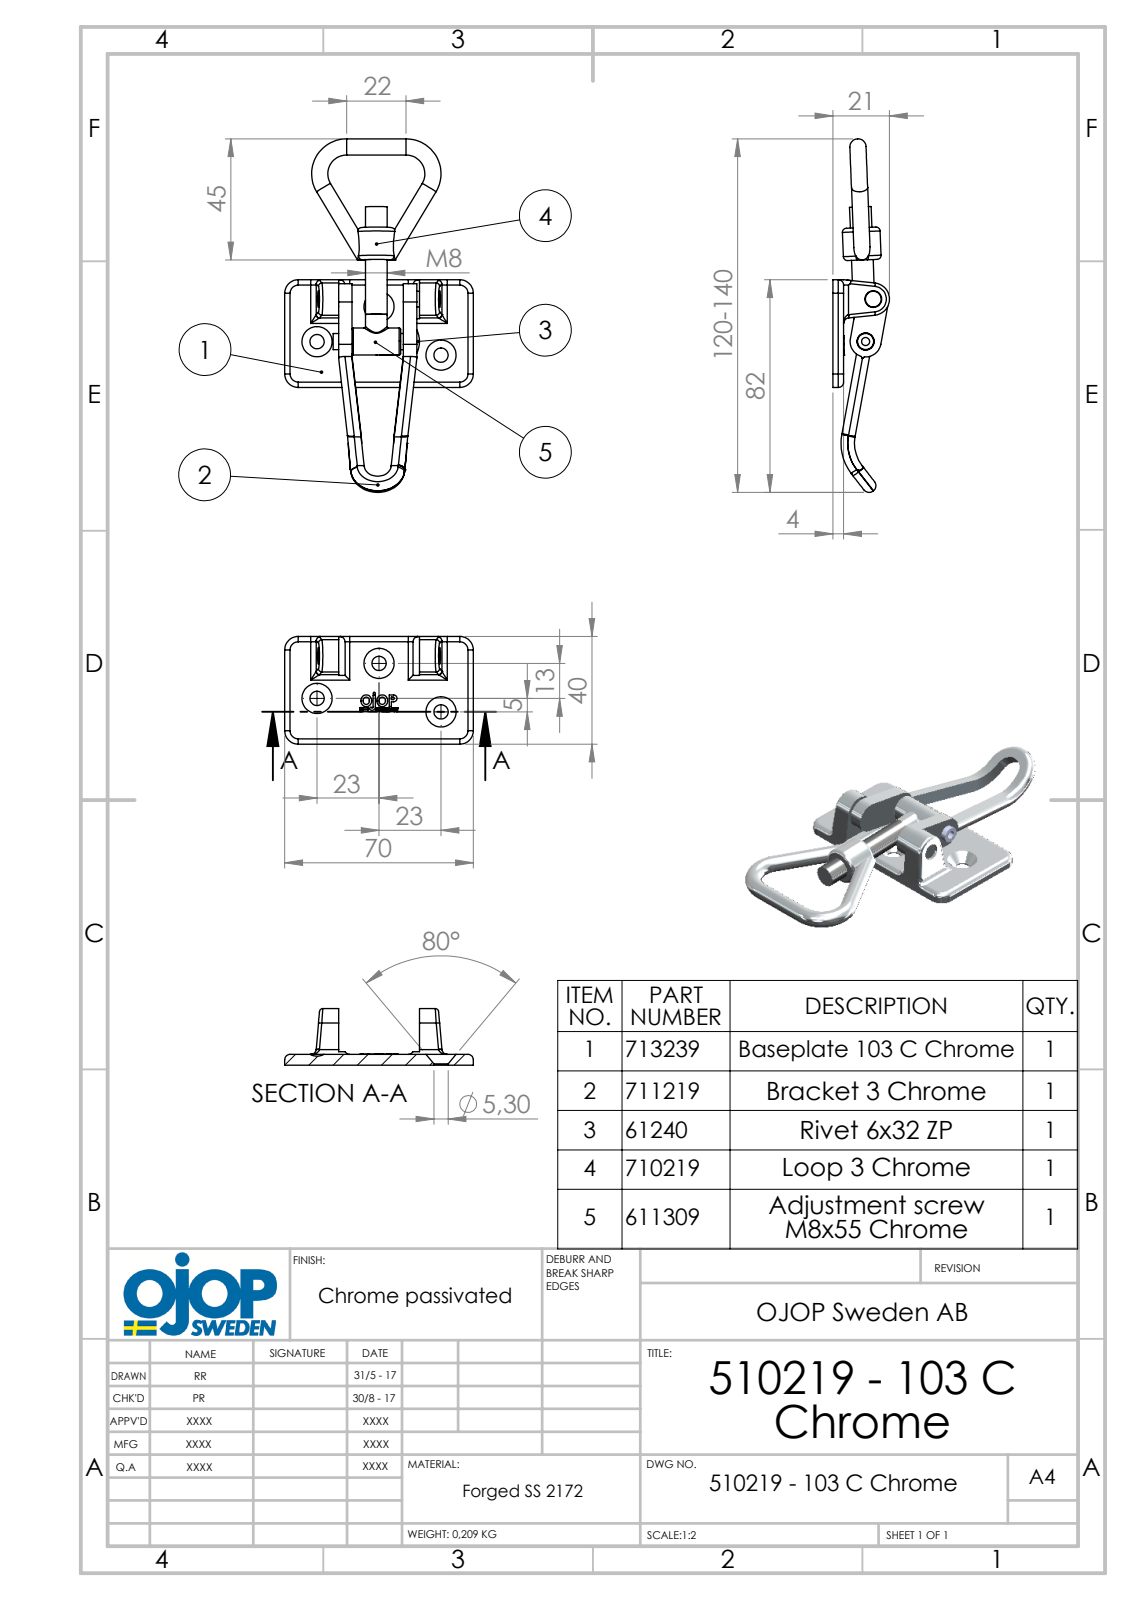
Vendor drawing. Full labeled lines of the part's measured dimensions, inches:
Part name (STEP PRODUCT): bygel 3; 103 C; 510219 - 103 C Kromad; Justerskruv M8 (+3 more)
STEP written by: SolidWorks 2015 (AUTOMOTIVE_DESIGN)
Units: inches
Bodies: 6 solids, 218 faces (62 planar, 89 cylindrical, 67 other)
Overall size (bounding box): 5.437 × 2.756 × 0.833
Volume: 1.702 in³ · Surface area: 28.24 in²
Round holes (diameter × count): ⌀0.209 ×3, ⌀0.244 ×2, ⌀0.319 ×2, ⌀0.118 ×1, ⌀0.248 ×1
Round bosses / shafts (diameter × count): ⌀0.236 ×4, ⌀0.394 ×1, ⌀0.315 ×1, ⌀0.315 ×1, ⌀0.23 ×1
Partial cylindrical surfaces — rounded edges, fillets, slot ends (radius × count): R0.079 ×9, R0.098 ×8, R0.197 ×5, R0.049 ×4, R0.275 ×4, R0.059 ×2, R0.242 ×2, R0.094 ×1
Main face-to-face distances: 0.157, 0.197, 0.984, 1.181, 0.787, 0.039, 0.484, 0.342, 0.143, 0.145
Hole centre spacings: 0.63, 1.04, 1.15, 1.822
